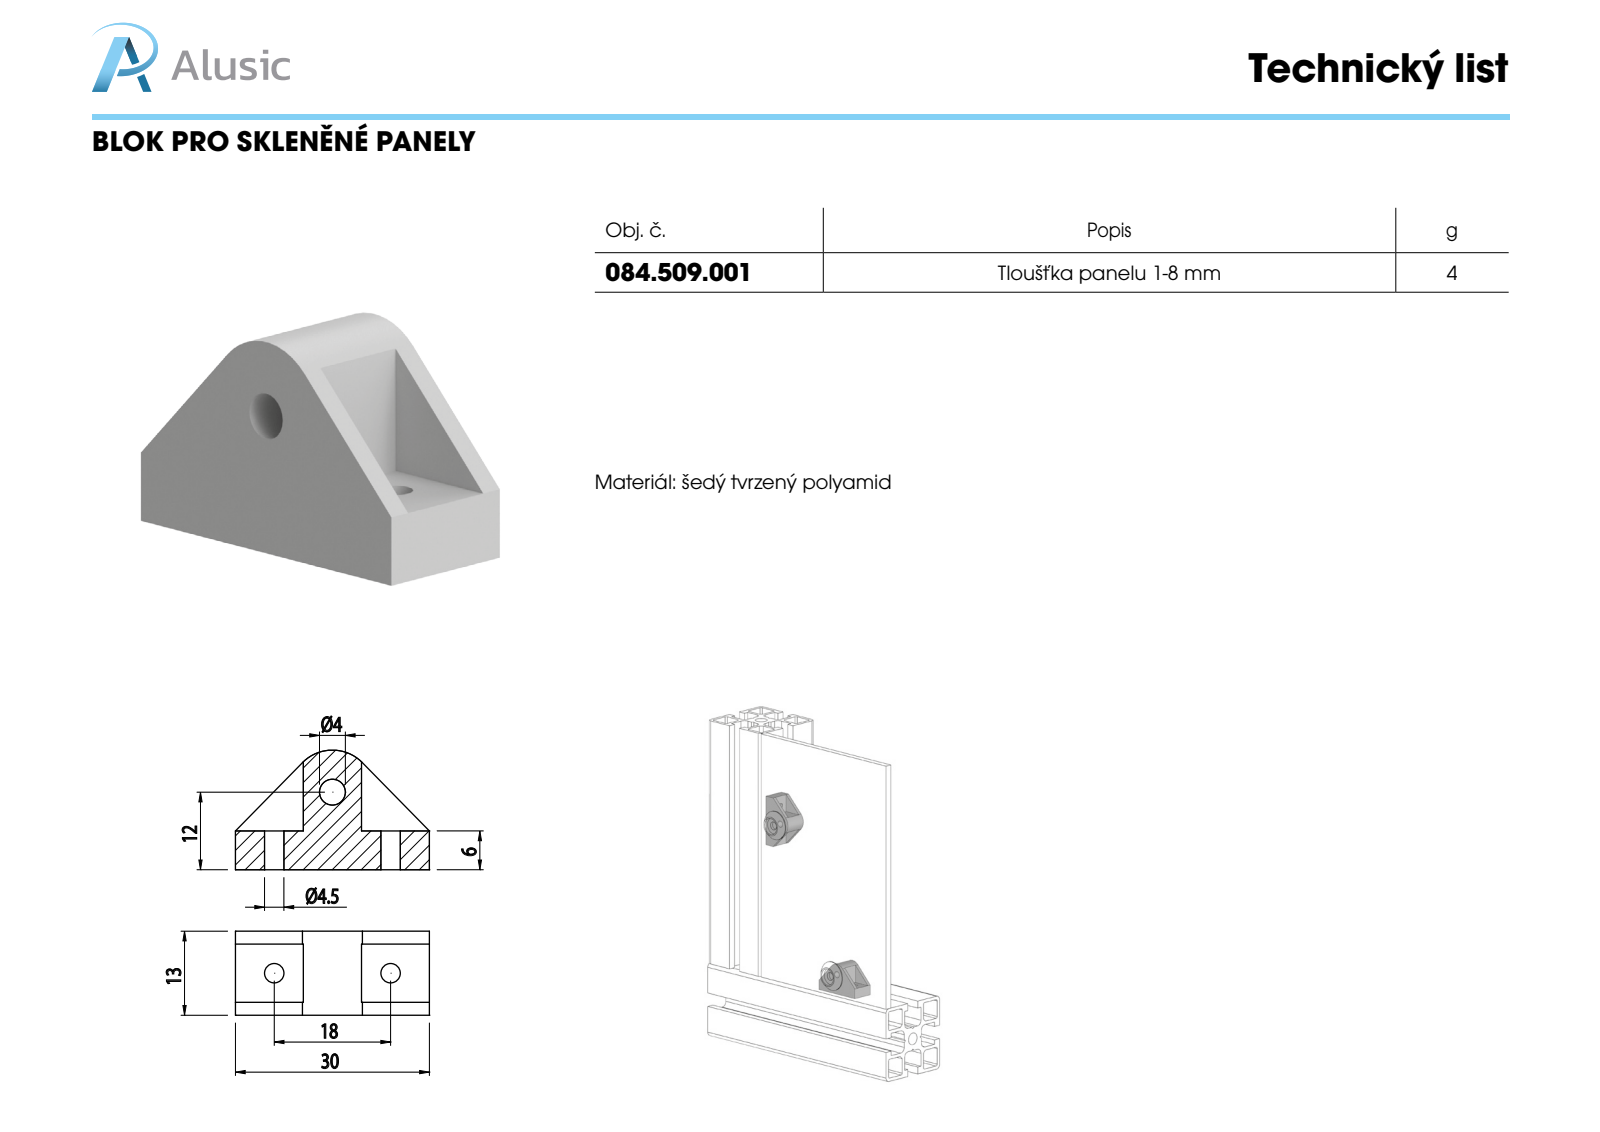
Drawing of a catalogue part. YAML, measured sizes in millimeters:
part_name: "084.509.001"
step_written_by: "SolidWorks 2011 (CONFIG_CONTROL_DESIGN)"
units: millimeters
bodies: {solids: 1, faces: 24, planar: 17, cylindrical: 7, other: 0}
overall_size: [30, 18.5, 13]
volume: 3937
surface_area: 2424
round_holes:
  - {diameter: 3, count: 2}
  - {diameter: 4, count: 1}
partial_cylinders:
  - {radius: 6.5, count: 1}
face_to_face_distances: [13, 2, 11, 9, 6, 10.5, 19.5, 30]
hole_center_spacings: [18]
